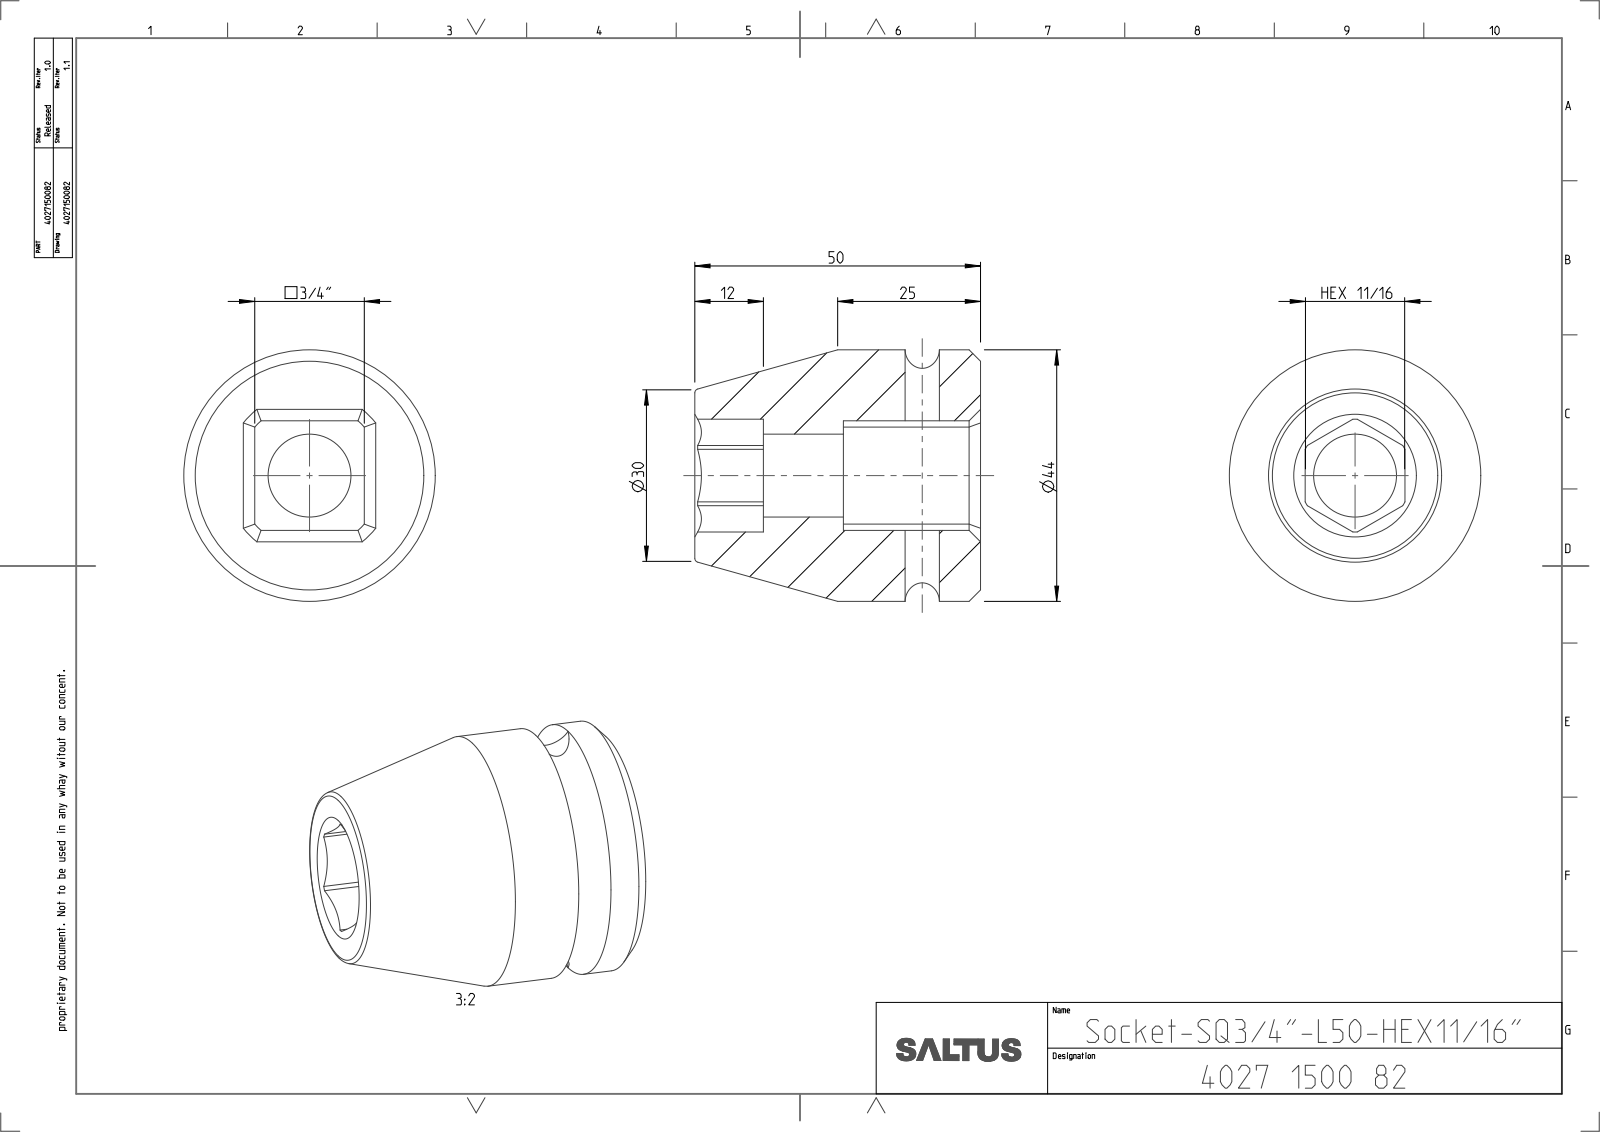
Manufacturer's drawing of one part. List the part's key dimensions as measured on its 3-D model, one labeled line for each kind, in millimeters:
Part name (STEP PRODUCT): 4027150082
STEP written by: CREO PARAMETRIC BY PTC INC, 2022414 (CONFIG_CONTROL_DESIGN)
Units: millimetres
Bodies: 1 solid, 52 faces (18 planar, 20 cylindrical, 14 other)
Overall size (bounding box): 50 × 44 × 44
Volume: 48 104 mm³ · Surface area: 11 826 mm²
Round holes (diameter × count): ⌀6 ×1, ⌀14.5 ×1
Round bosses / shafts (diameter × count): ⌀44 ×1
Partial cylindrical surfaces — rounded edges, fillets, slot ends (radius × count): R9.87 ×1, R12.8 ×1
Main face-to-face distances: 19.18, 17.46, 50, 0.86, 18.32, 24, 26, 38, 14, 12
